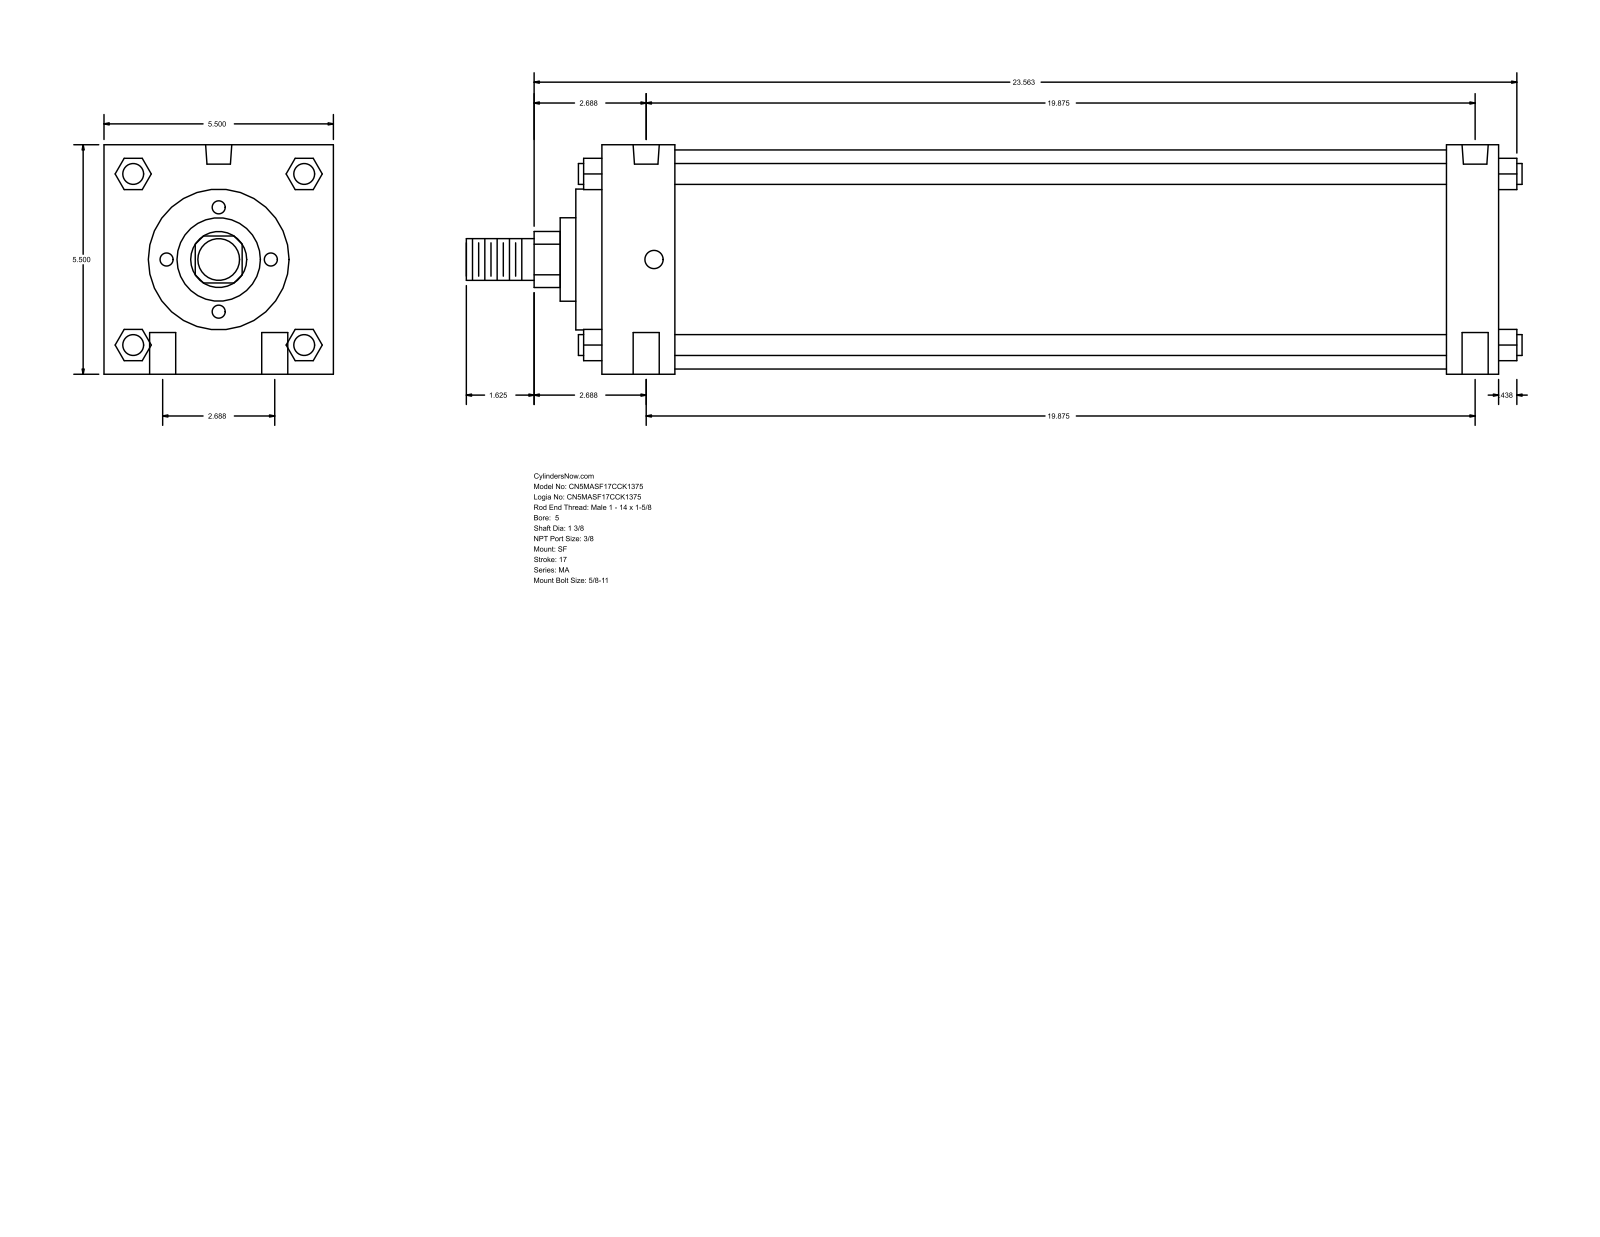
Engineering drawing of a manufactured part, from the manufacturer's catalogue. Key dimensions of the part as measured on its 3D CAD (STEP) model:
Part name (STEP PRODUCT): MA_SF__0500_1.375
STEP written by: GSSL Pune (CONFIG_CONTROL_DESIGN)
Units: millimetres
Bodies: 0 solids, 126 faces (95 planar, 31 cylindrical, 0 other)
Overall size (bounding box): 642.94 × 139.7 × 139.7
Round holes (diameter × count): ⌀15.88 ×4, ⌀11.11 ×2, ⌀15.93 ×2
Round bosses / shafts (diameter × count): ⌀12.7 ×4, ⌀133.35 ×1, ⌀85.72 ×1, ⌀50.8 ×1, ⌀34.92 ×1, ⌀25.4 ×1
Partial cylindrical surfaces — rounded edges, fillets, slot ends (radius × count): R17.06 ×1
Main face-to-face distances: 139.7, 546.11, 44.45, 514.35, 469.9, 501.66, 31.76, 15.87, 60.32, 530.22
Hole centre spacings: 34.13, 505.98, 504.83, 68.26, 509.42, 495.3
